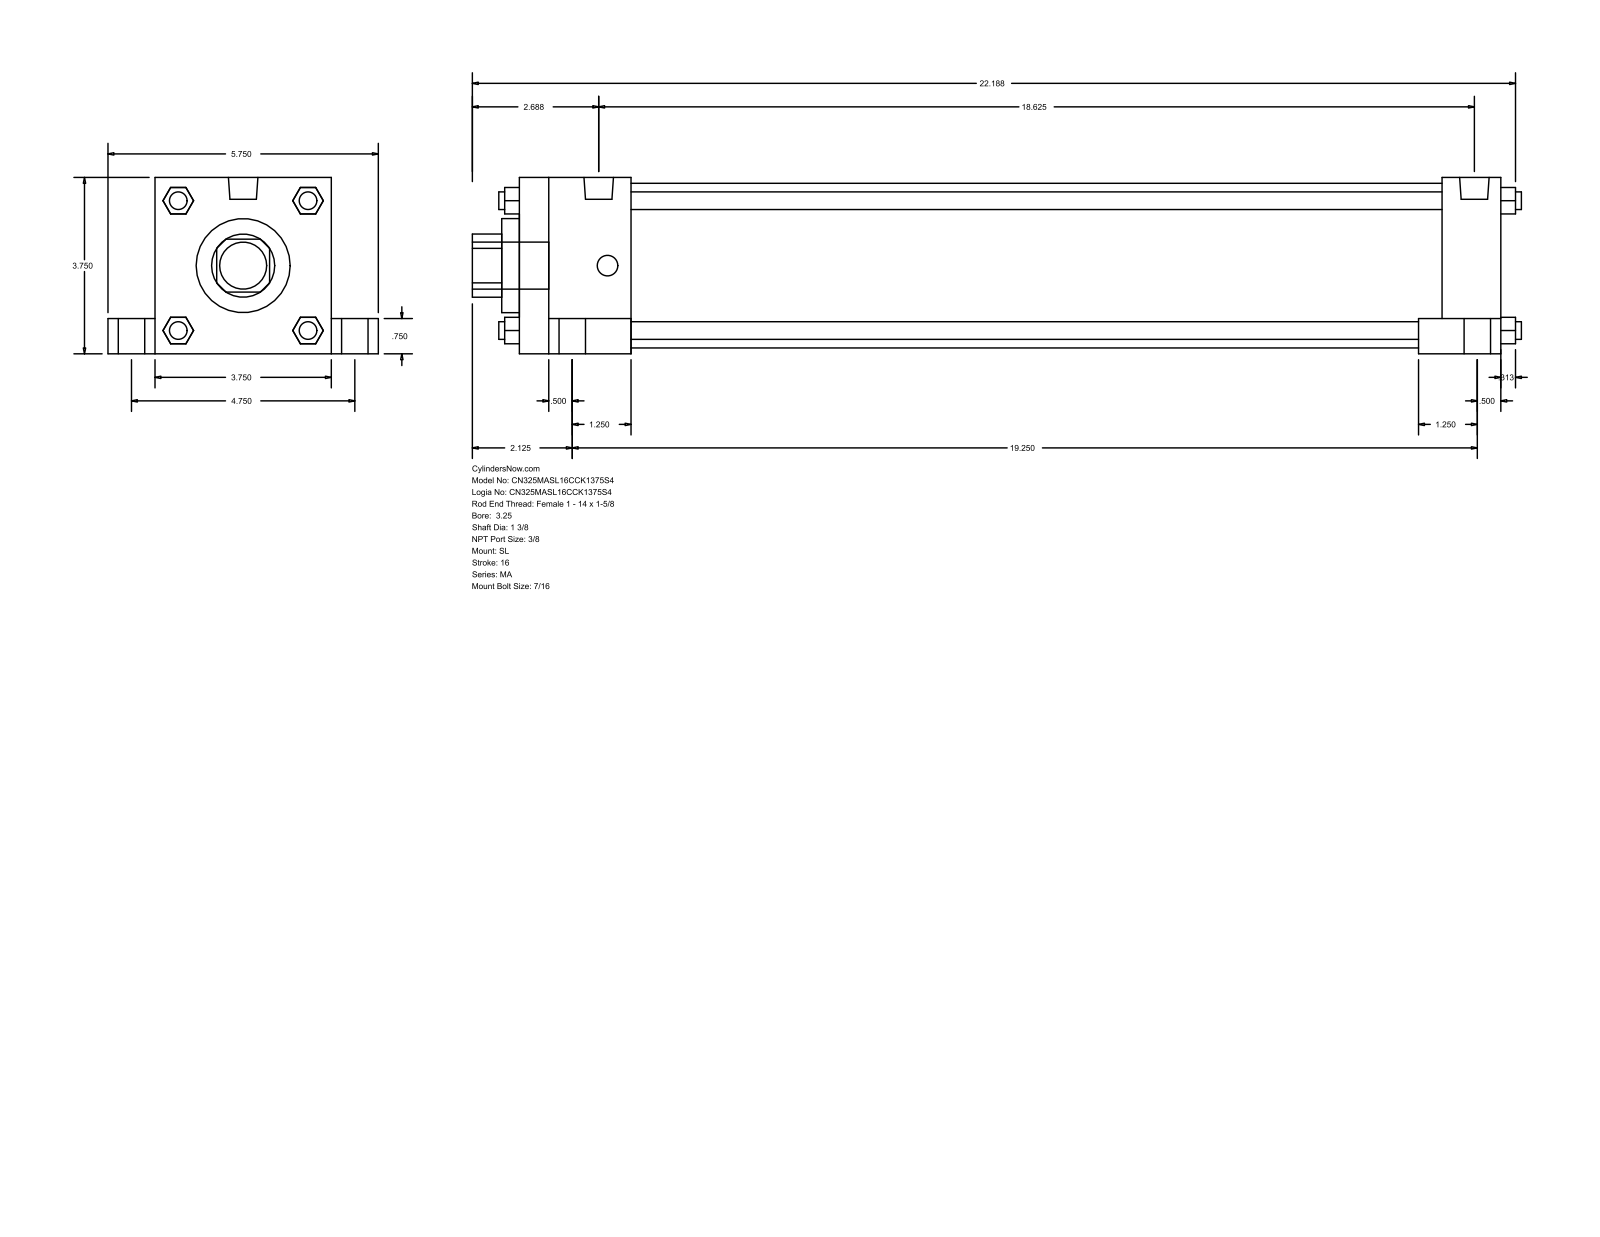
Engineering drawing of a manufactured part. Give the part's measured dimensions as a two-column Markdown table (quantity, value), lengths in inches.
| quantity | value |
| --- | --- |
| part name | MA_SL__0325_1.375 |
| STEP written by | GSSL Pune (CONFIG_CONTROL_DESIGN) |
| units | inches |
| bodies | 0 solids, 148 faces (112 planar, 36 cylindrical, 0 other) |
| overall size | 22.313 × 5.75 × 3.75 |
| round holes (diameter × count) | 1.375 × 1, 2 × 1, 3.5 × 1 |
| round bosses / shafts (diameter × count) | 0.813 × 4, 0.563 × 4, 0.437 × 4, 0.375 × 4, 0.627 × 2, 1 × 1 |
| partial cylindrical surfaces (radius × count) | 0.672 × 1 |
| main face-to-face distances | 3.75, 20.875, 1, 4.75, 19.625, 1.25, 2.375, 17.25, 18.5, 0.75 |
